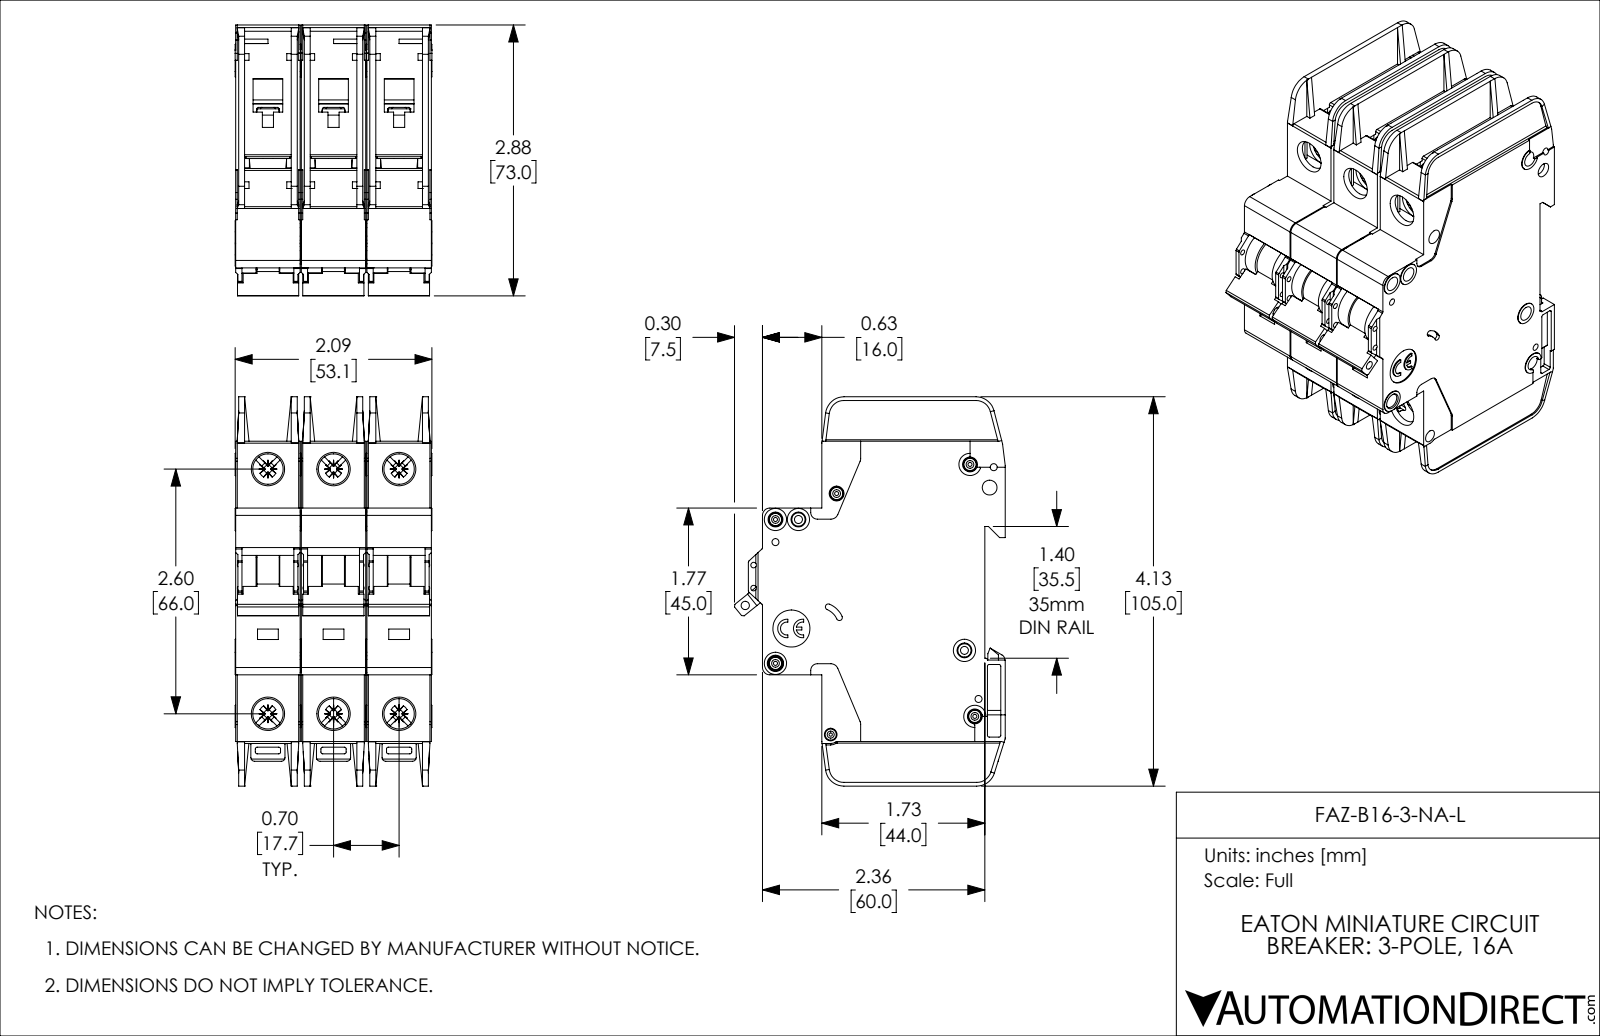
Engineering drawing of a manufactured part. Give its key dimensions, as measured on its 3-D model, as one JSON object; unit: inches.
{"part_name": "FAZ-B16-3-NA-L", "step_written_by": "SolidWorks 2019 (AUTOMOTIVE_DESIGN)", "units": "inches", "bodies": {"solids": 3, "faces": 3381, "planar": 2013, "cylindrical": 1071, "other": 297}, "overall_size": [4.134, 2.876, 2.091], "volume_in3": 14.05, "surface_area_in2": 123, "round_holes": [[0.157, 8], [0.323, 6], [0.043, 5], [0.075, 4], [0.059, 2], [0.085, 2], [0.035, 1], [0.089, 1], [0.098, 1], [0.134, 1], [0.394, 1]], "round_bosses_or_shafts": [[0.13, 5], [0.236, 4], [0.118, 4], [0.098, 3]], "partial_cylinders_radius": [[0.02, 72], [0.016, 30], [0.039, 18], [0.043, 12], [0.079, 12], [0.008, 6], [0.01, 6], [0.028, 6]], "face_to_face_distances": [0.697, 0.047, 1.394, 0.685, 0.591, 1.382, 0.744, 0.65, 0.106, 0.094], "hole_center_spacings": [0.697, 2.69, 2.598, 0.244, 0.537, 0.87, 1.394, 2.948]}
